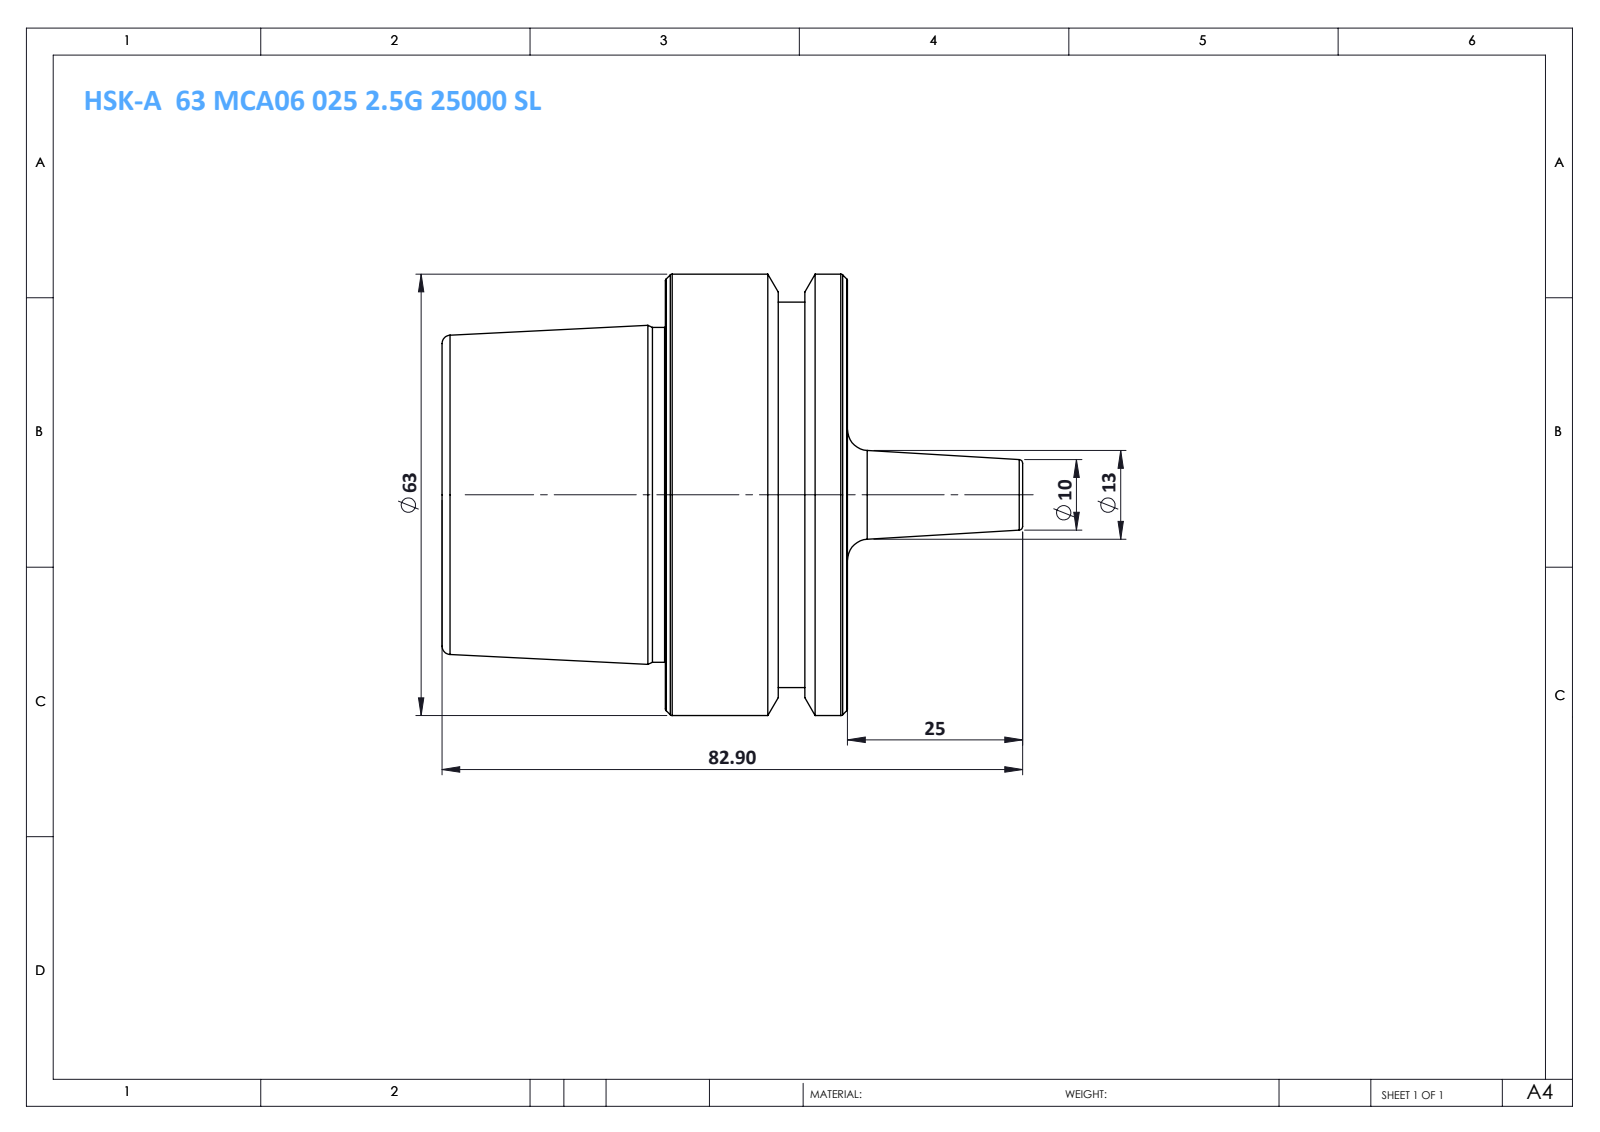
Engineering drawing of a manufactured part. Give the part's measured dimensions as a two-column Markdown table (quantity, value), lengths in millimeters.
| quantity | value |
| --- | --- |
| part name | HSK-A 63 MCA06 025 2.5G 25000 SL |
| STEP written by | SolidWorks 2014 (CONFIG_CONTROL_DESIGN) |
| units | millimeters |
| bodies | 1 solid, 46 faces (6 planar, 8 cylindrical, 32 other) |
| overall size | 82.9 × 63 × 63 |
| volume | 135 281 mm³ |
| surface area | 17 452 mm² |
| round bosses / shafts (diameter × count) | 63 × 1, 55 × 1, 47.78 × 1 |
| main face-to-face distances | 57.9, 26, 31.9, 6.1, 19.9, 51.8, 9.9, 3.8, 16.1, 48 |
